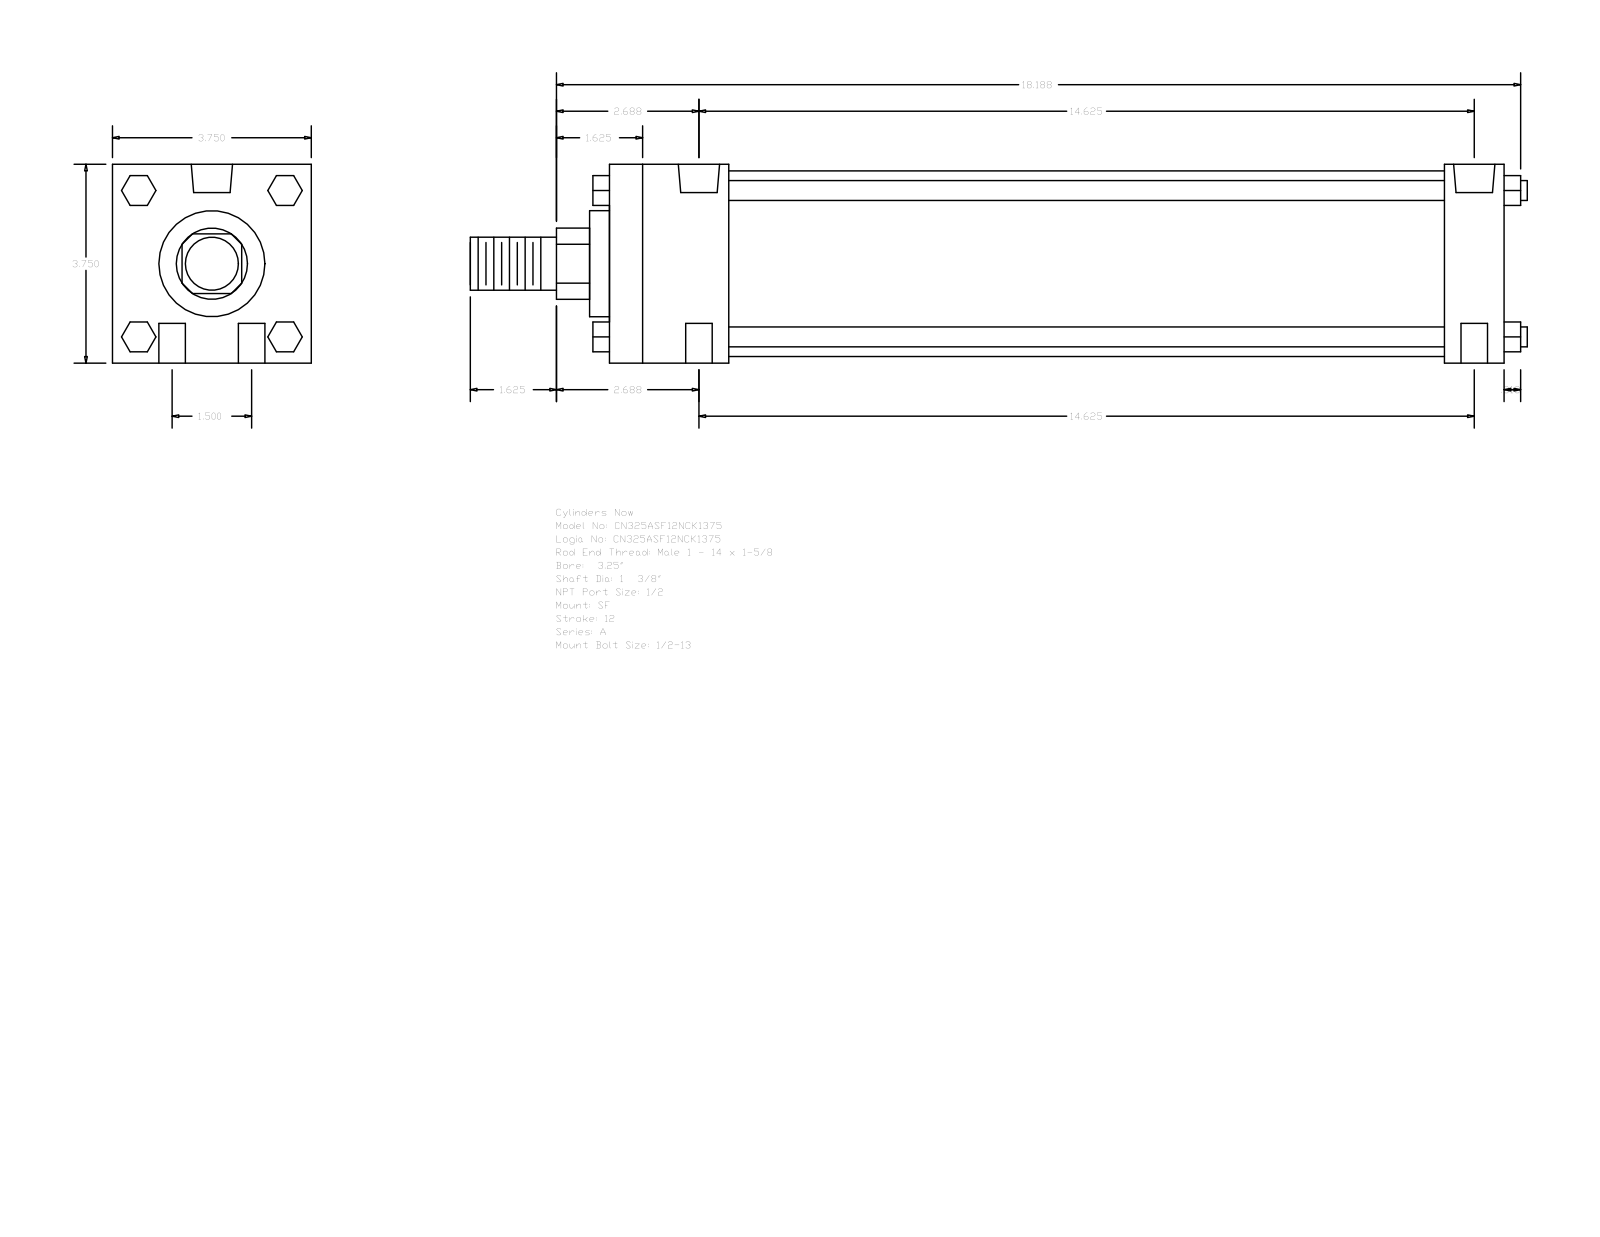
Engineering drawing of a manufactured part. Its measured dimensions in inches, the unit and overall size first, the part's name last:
Units: inches
Overall size (bounding box): 19.937 × 3.75 × 3.75
Round holes (diameter × count): ⌀0.5 ×4, ⌀0.344 ×2, ⌀0.778 ×2
Round bosses / shafts (diameter × count): ⌀0.375 ×4, ⌀3.5 ×1, ⌀2 ×1, ⌀1.375 ×1, ⌀1 ×1
Partial cylindrical surfaces — rounded edges, fillets, slot ends (radius × count): R0.672 ×1
Main face-to-face distances: 3.75, 16.875, 2.25, 15.75, 1.125, 13.5, 14.625, 2.625, 0.375, 16.125
Hole centre spacings: 0.75, 14.644, 14.625, 1.5, 14.702, 14.375
Bodies: 0 solids, 124 faces (94 planar, 30 cylindrical, 0 other)
Part name (STEP PRODUCT): A_SF__0325_1.375
STEP written by: GSSL Pune (CONFIG_CONTROL_DESIGN)
